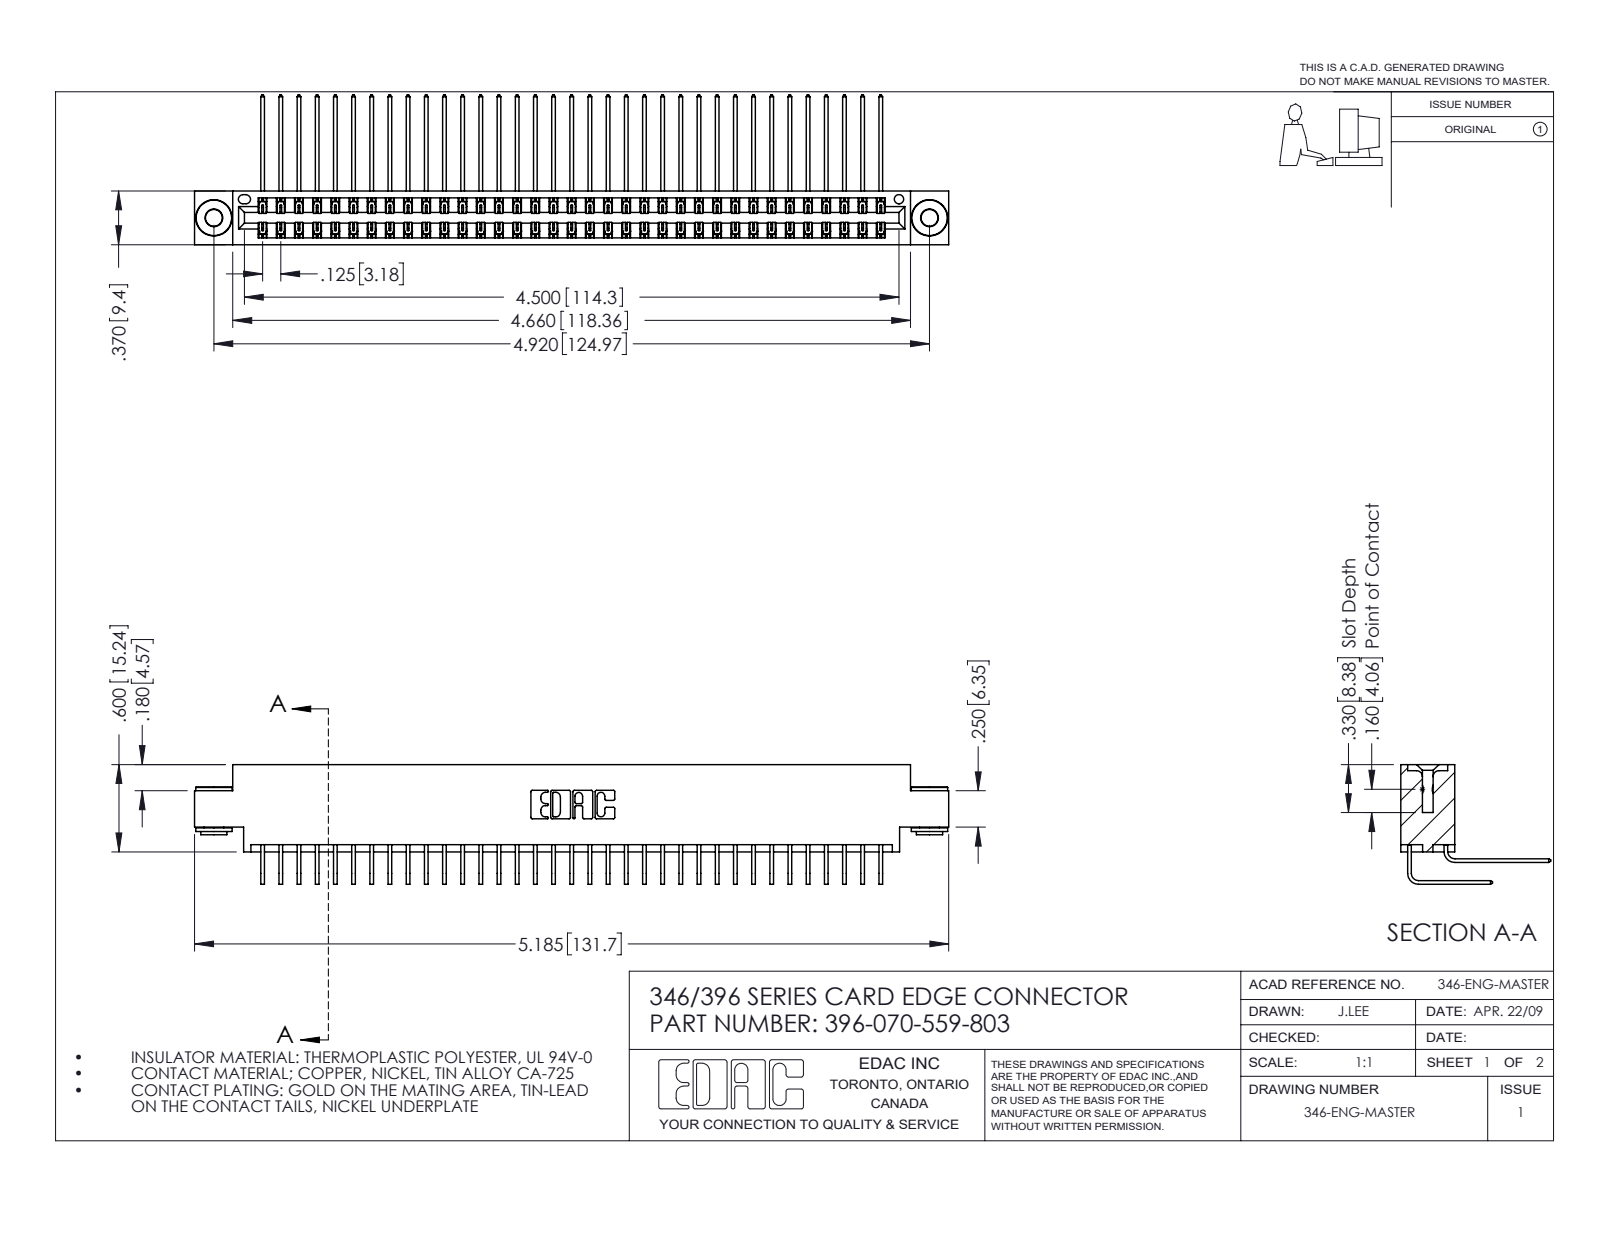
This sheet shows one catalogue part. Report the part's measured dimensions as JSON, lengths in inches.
{"part_name": "345-292-001_558 559 Tail - 1; 396-070-559-803; 345-292-001_559 Tail - 2; 346 Part_0.170 Offset - 0.156 Dia-TH (+1 more)", "step_written_by": "SolidWorks 2016 (CONFIG_CONTROL_DESIGN)", "units": "inches", "bodies": {"solids": 73, "faces": 3944, "planar": 2680, "cylindrical": 1256, "other": 8}, "overall_size": [5.185, 1.03, 0.823], "volume_in3": 0.797, "surface_area_in2": 31.26, "round_holes": [[0.116, 2], [0.156, 2], [0.064, 1]], "round_bosses_or_shafts": [[0.25, 2], [0.18, 2], [0.136, 2]], "partial_cylinders_radius": [[0.006, 105], [0.01, 22], [0.007, 6], [0.031, 6], [0.026, 3], [0.014, 2], [0.022, 2], [0.024, 2]], "face_to_face_distances": [0.048, 0.322, 0.025, 0.37, 0.25, 0.072, 0.298, 0.275, 0.15, 0.148], "hole_center_spacings": [0.246, 4.711, 4.92]}
